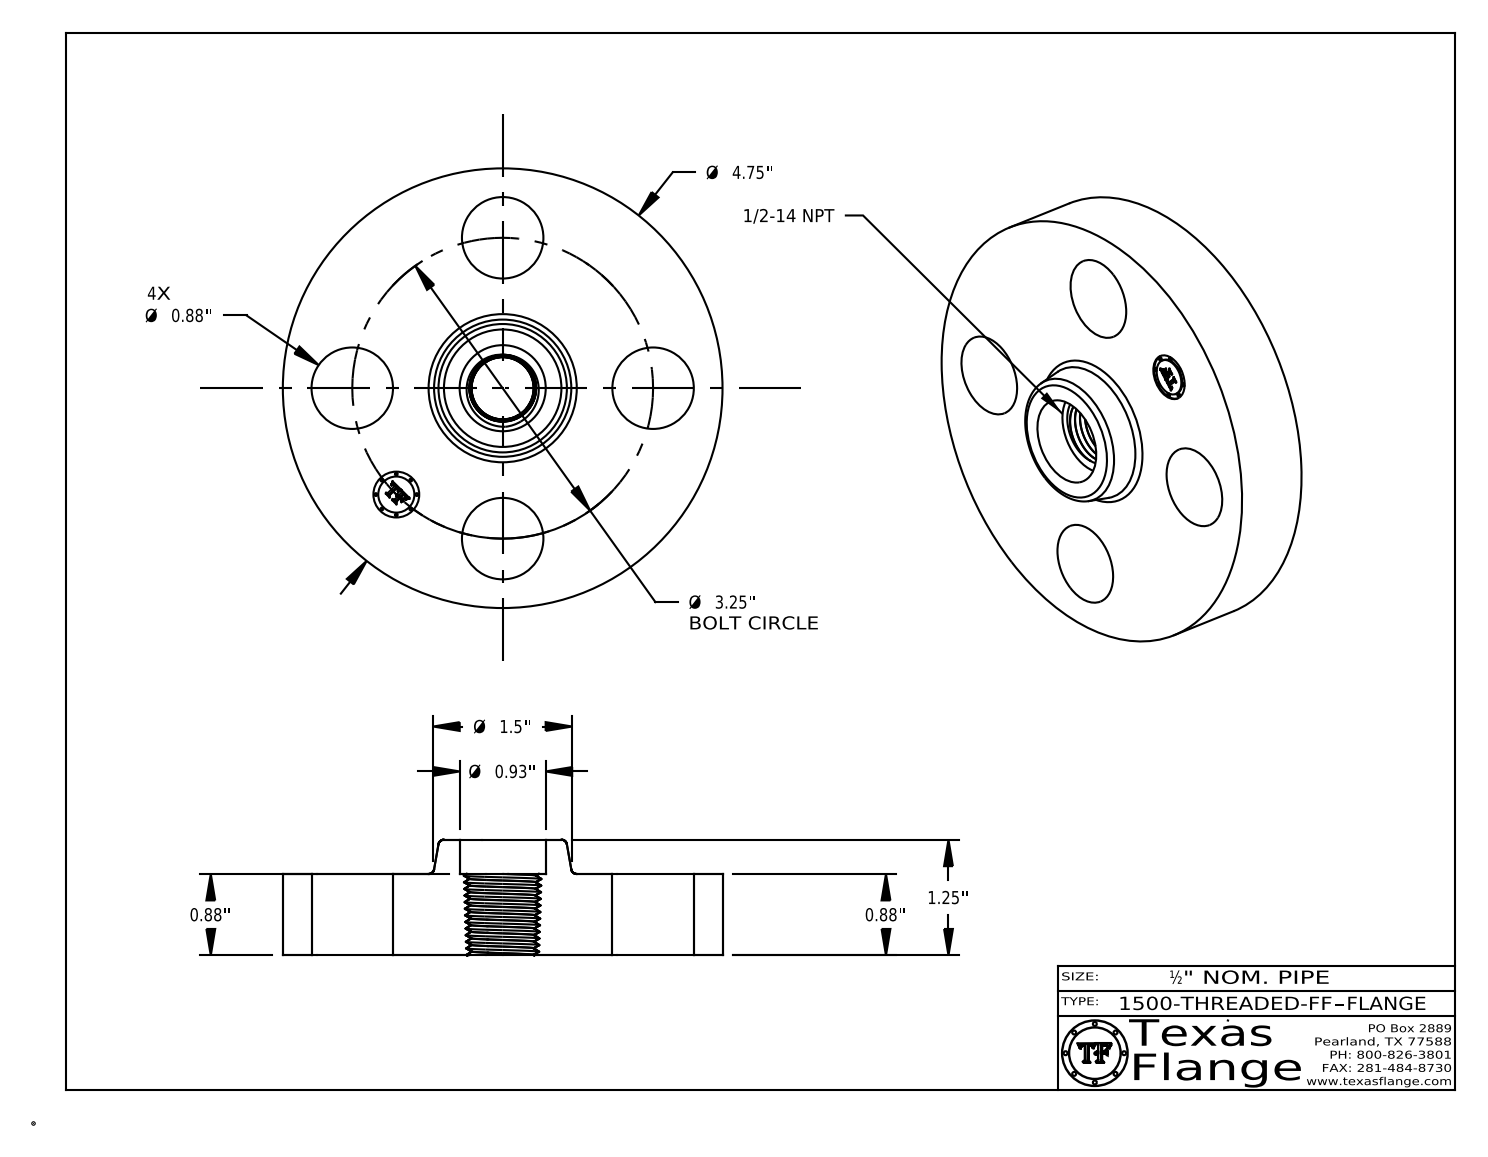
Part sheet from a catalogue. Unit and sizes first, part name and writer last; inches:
Units: inches
Overall size (bounding box): 4.75 × 4.75 × 1.25
Round holes (diameter × count): ⌀0.88 ×4, ⌀0.495 ×1, ⌀0.93 ×1
Round bosses / shafts (diameter × count): ⌀0.03 ×8, ⌀4.75 ×1, ⌀0.39 ×1
Main face-to-face distances: 0.88, 1.25, 0.37, 0.865, 0.015, 0.385, 0.148, 0.144, 0.027, 0.096
Hole centre spacings: 1.625, 2.298, 1.244, 3.003, 3.25
Volume: 13.41 in³ · Surface area: 58.85 in²
Bodies: 1 solid, 535 faces (369 planar, 32 cylindrical, 134 other)
Part name (STEP PRODUCT): 1500-THREADED-FF
STEP written by: CATIA V5 STEP AP214 (AUTOMOTIVE_DESIGN)
